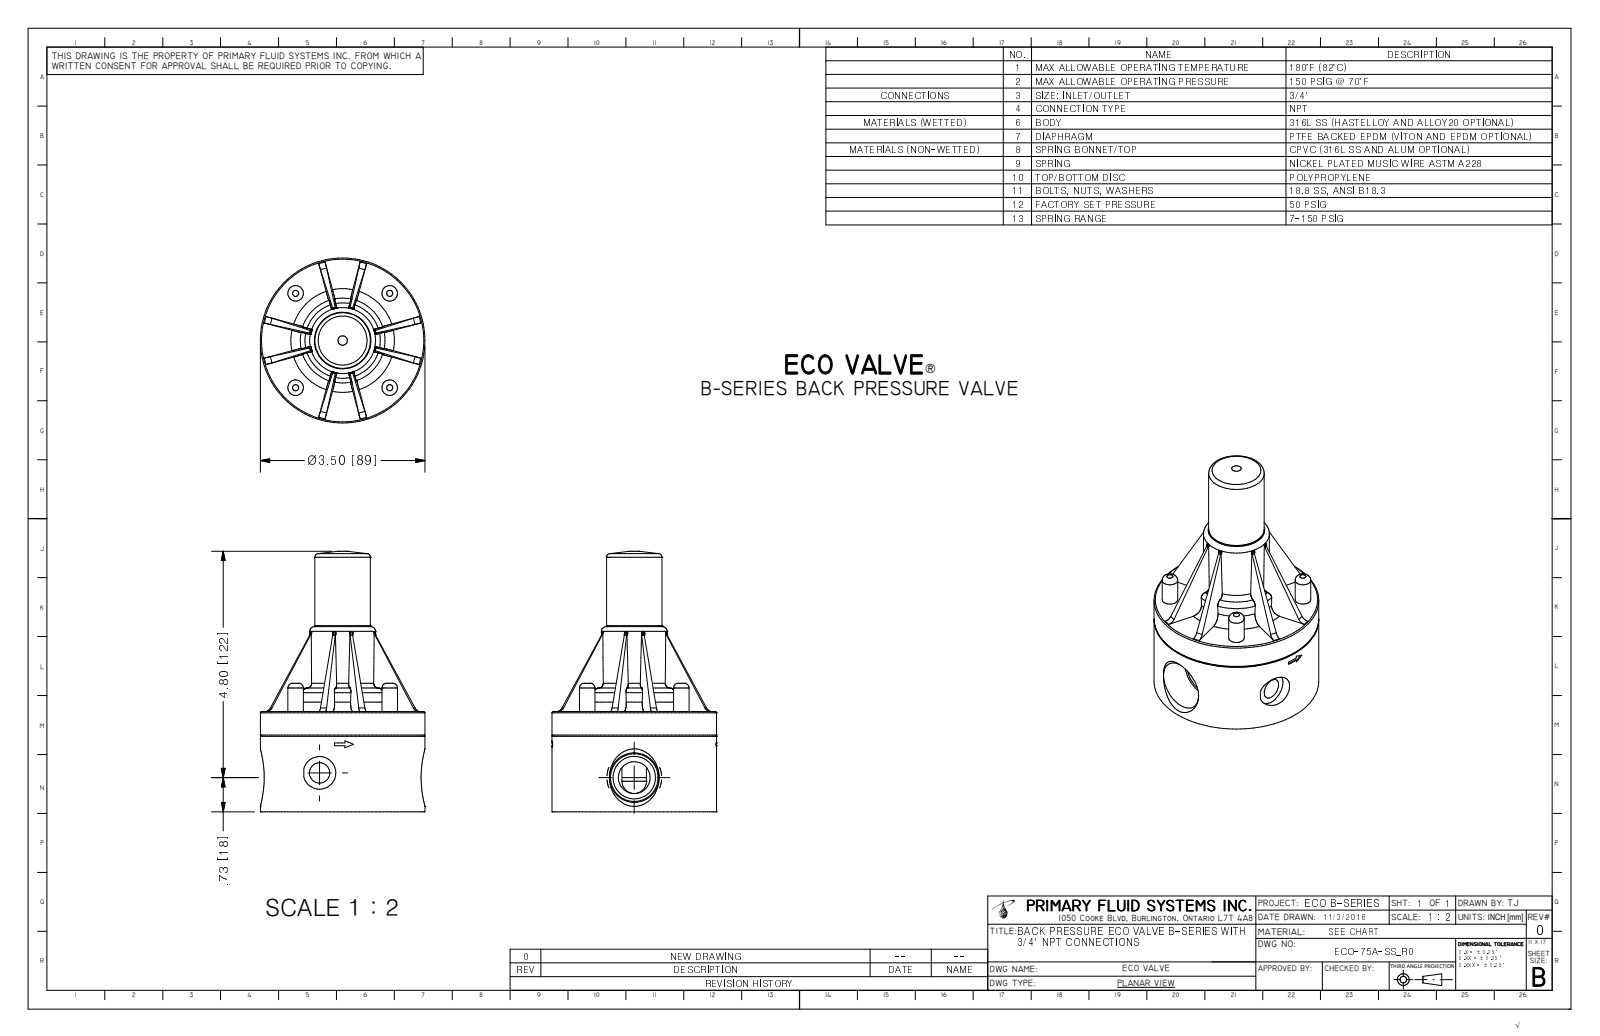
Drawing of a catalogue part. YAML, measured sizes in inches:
part_name: "ECO-75A-SS_R0"
step_written_by: "Autodesk Inventor 2009 (AUTOMOTIVE_DESIGN)"
units: inches
bodies: {solids: 1, faces: 167, planar: 70, cylindrical: 39, other: 58}
overall_size: [5.525, 3.5, 3.5]
volume: 24.8
surface_area: 80.01
round_holes:
  - {diameter: 0.23, count: 2}
  - {diameter: 0.256, count: 2}
  - {diameter: 0.257, count: 2}
  - {diameter: 0.4, count: 2}
  - {diameter: 0.431, count: 2}
  - {diameter: 0.691, count: 2}
round_bosses_or_shafts:
  - {diameter: 0.33, count: 4}
  - {diameter: 3.5, count: 1}
  - {diameter: 1.8, count: 1}
  - {diameter: 1.4, count: 1}
  - {diameter: 1.18, count: 1}
partial_cylinders:
  - {radius: 0.15, count: 8}
  - {radius: 1.73, count: 1}
face_to_face_distances: [2.125, 2.09, 1.6, 0.27, 0.525, 3.086, 1.45, 2.325, 1.33, 1.855]
hole_center_spacings: [2.828]
